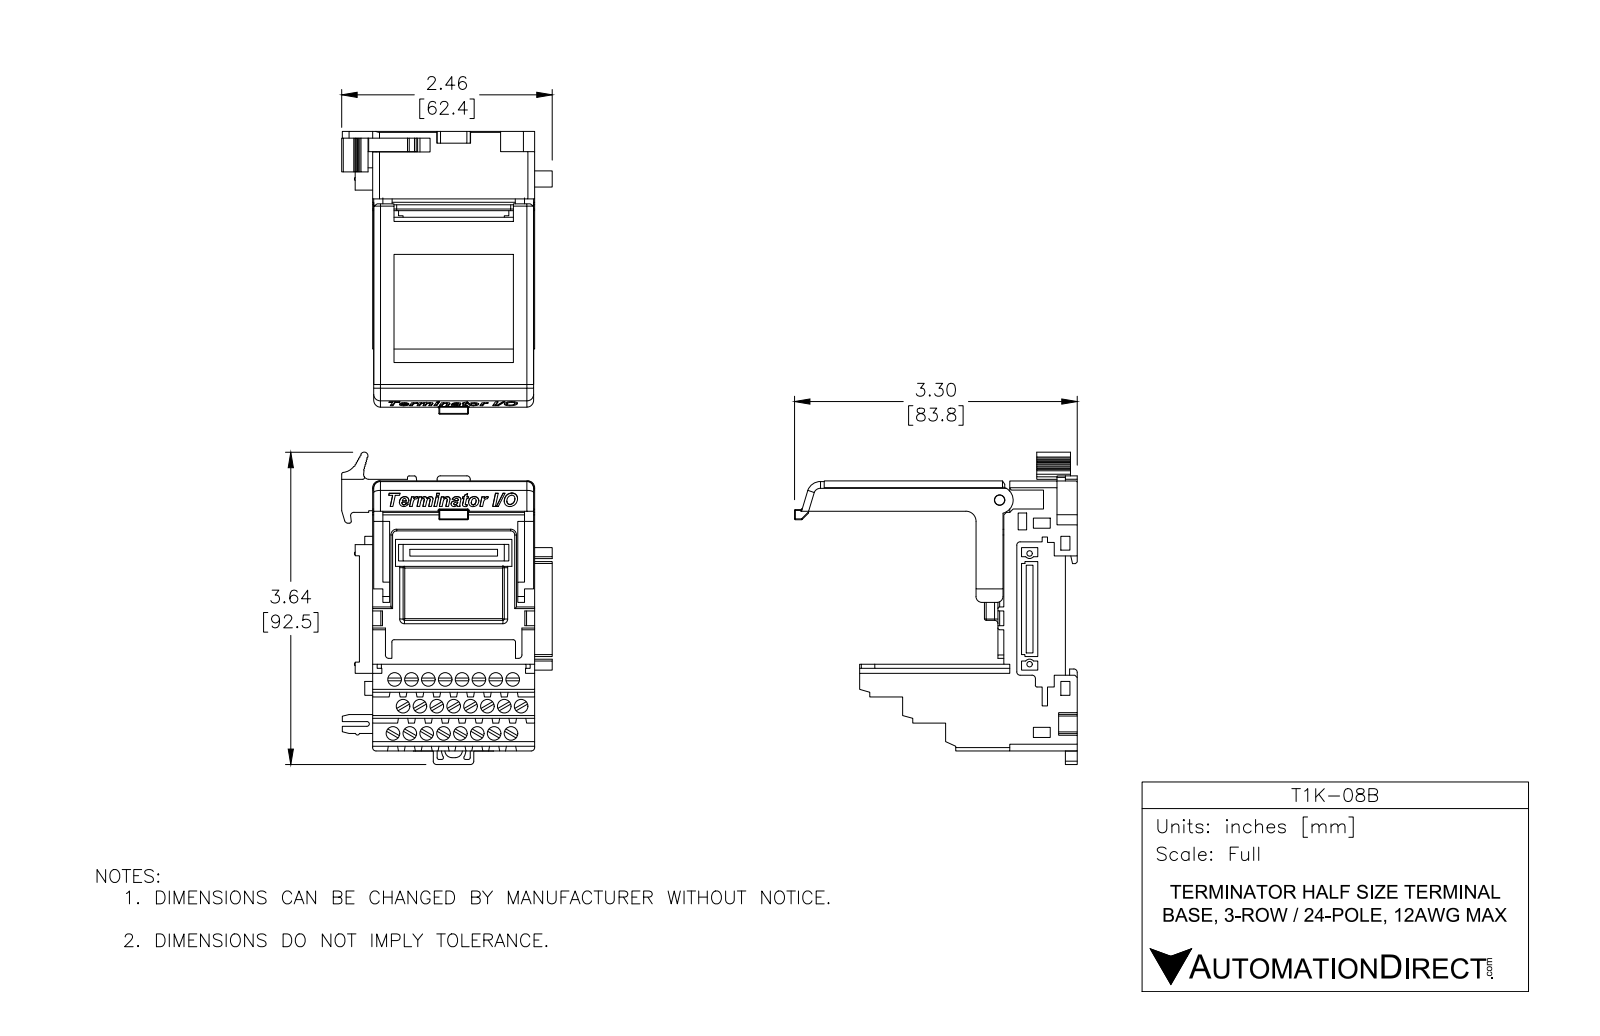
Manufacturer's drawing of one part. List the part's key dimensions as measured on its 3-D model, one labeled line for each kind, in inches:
Part name (STEP PRODUCT): T1K-08B
STEP written by: SolidWorks 2013 (AUTOMOTIVE_DESIGN)
Units: inches
Bodies: 36 solids, 1212 faces (955 planar, 152 cylindrical, 105 other)
Overall size (bounding box): 3.625 × 3.235 × 2.461
Volume: 8.087 in³ · Surface area: 71.37 in²
Round holes (diameter × count): ⌀0.157 ×24, ⌀0.063 ×2
Round bosses / shafts (diameter × count): ⌀0.059 ×2
Partial cylindrical surfaces — rounded edges, fillets, slot ends (radius × count): R0.039 ×14, R0.079 ×13, R0.03 ×8, R0.081 ×2, R0.033 ×1, R0.08 ×1, R0.08 ×1, R0.138 ×1
Main face-to-face distances: 0.079, 1.89, 0.138, 0.74, 2.136, 0.661, 0.878, 0.157, 0.799, 1.014
Hole centre spacings: 0.202, 0.356, 0.404, 0.203, 0.357, 0.455, 0.641, 0.202
